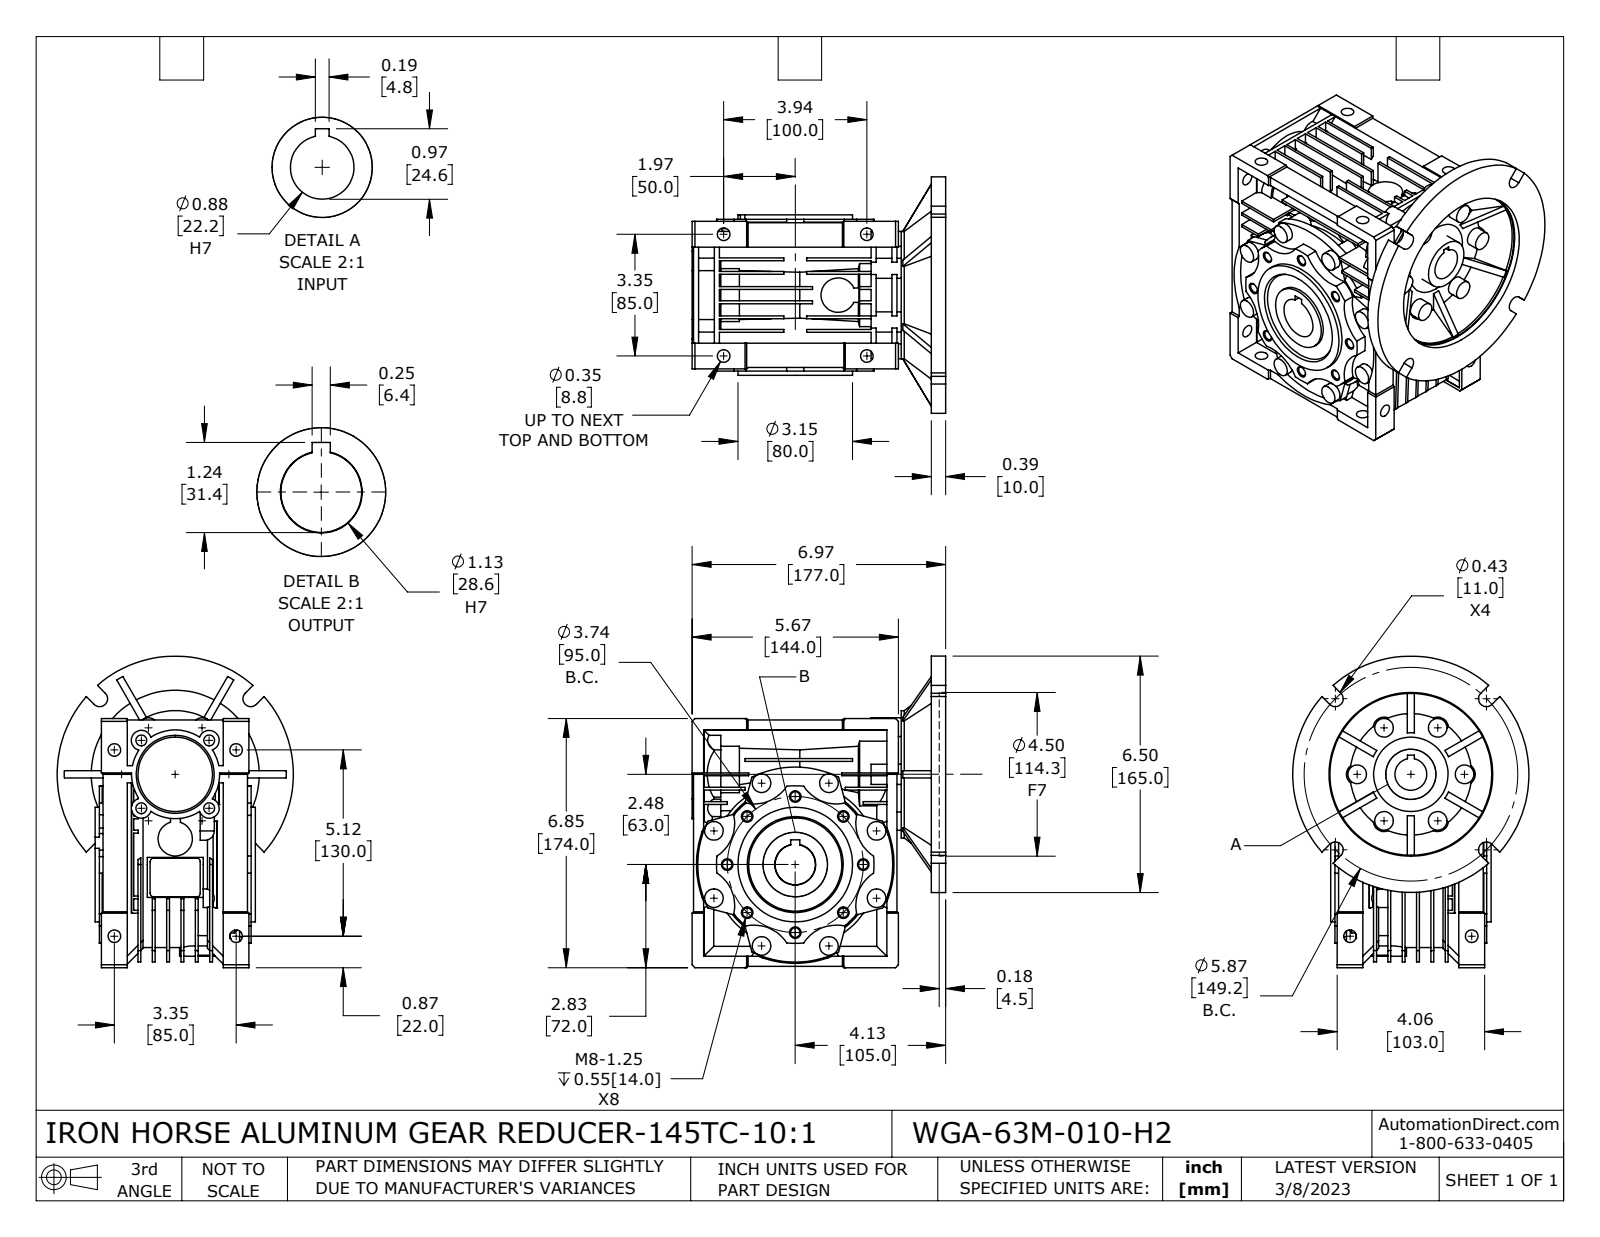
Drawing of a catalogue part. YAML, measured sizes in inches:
part_name: "WGA-63M-010-H2"
step_written_by: "SolidWorks 2021 (CONFIG_CONTROL_DESIGN)"
units: inches
bodies: {solids: 4, faces: 1230, planar: 759, cylindrical: 331, other: 140}
overall_size: [8.563, 6.969, 6.496]
volume: 116.3
surface_area: 570.4
round_holes:
  - {diameter: 0.262, count: 8}
  - {diameter: 0.262, count: 8}
  - {diameter: 0.346, count: 8}
  - {diameter: 0.298, count: 4}
  - {diameter: 0.875, count: 1}
  - {diameter: 0.906, count: 1}
  - {diameter: 1.125, count: 1}
  - {diameter: 1.339, count: 1}
  - {diameter: 1.457, count: 1}
  - {diameter: 1.772, count: 1}
  - {diameter: 2.047, count: 1}
  - {diameter: 4.449, count: 1}
round_bosses_or_shafts:
  - {diameter: 0.512, count: 14}
  - {diameter: 0.945, count: 3}
  - {diameter: 6.496, count: 1}
  - {diameter: 4.331, count: 1}
  - {diameter: 3.504, count: 1}
  - {diameter: 3.15, count: 1}
  - {diameter: 2.717, count: 1}
  - {diameter: 2.441, count: 1}
partial_cylinders:
  - {radius: 0.276, count: 10}
  - {radius: 1.063, count: 8}
  - {radius: 0.295, count: 6}
  - {radius: 0.098, count: 4}
  - {radius: 0.217, count: 4}
  - {radius: 0.329, count: 1}
  - {radius: 1.161, count: 1}
  - {radius: 1.201, count: 1}
face_to_face_distances: [0.394, 0.315, 0.787, 0.079, 1.181, 0.276, 0.472, 0.709, 1.575, 1.22]
hole_center_spacings: [1.431, 1.87, 2.645, 3.456, 1.319, 1.865, 3.346, 0.786]
